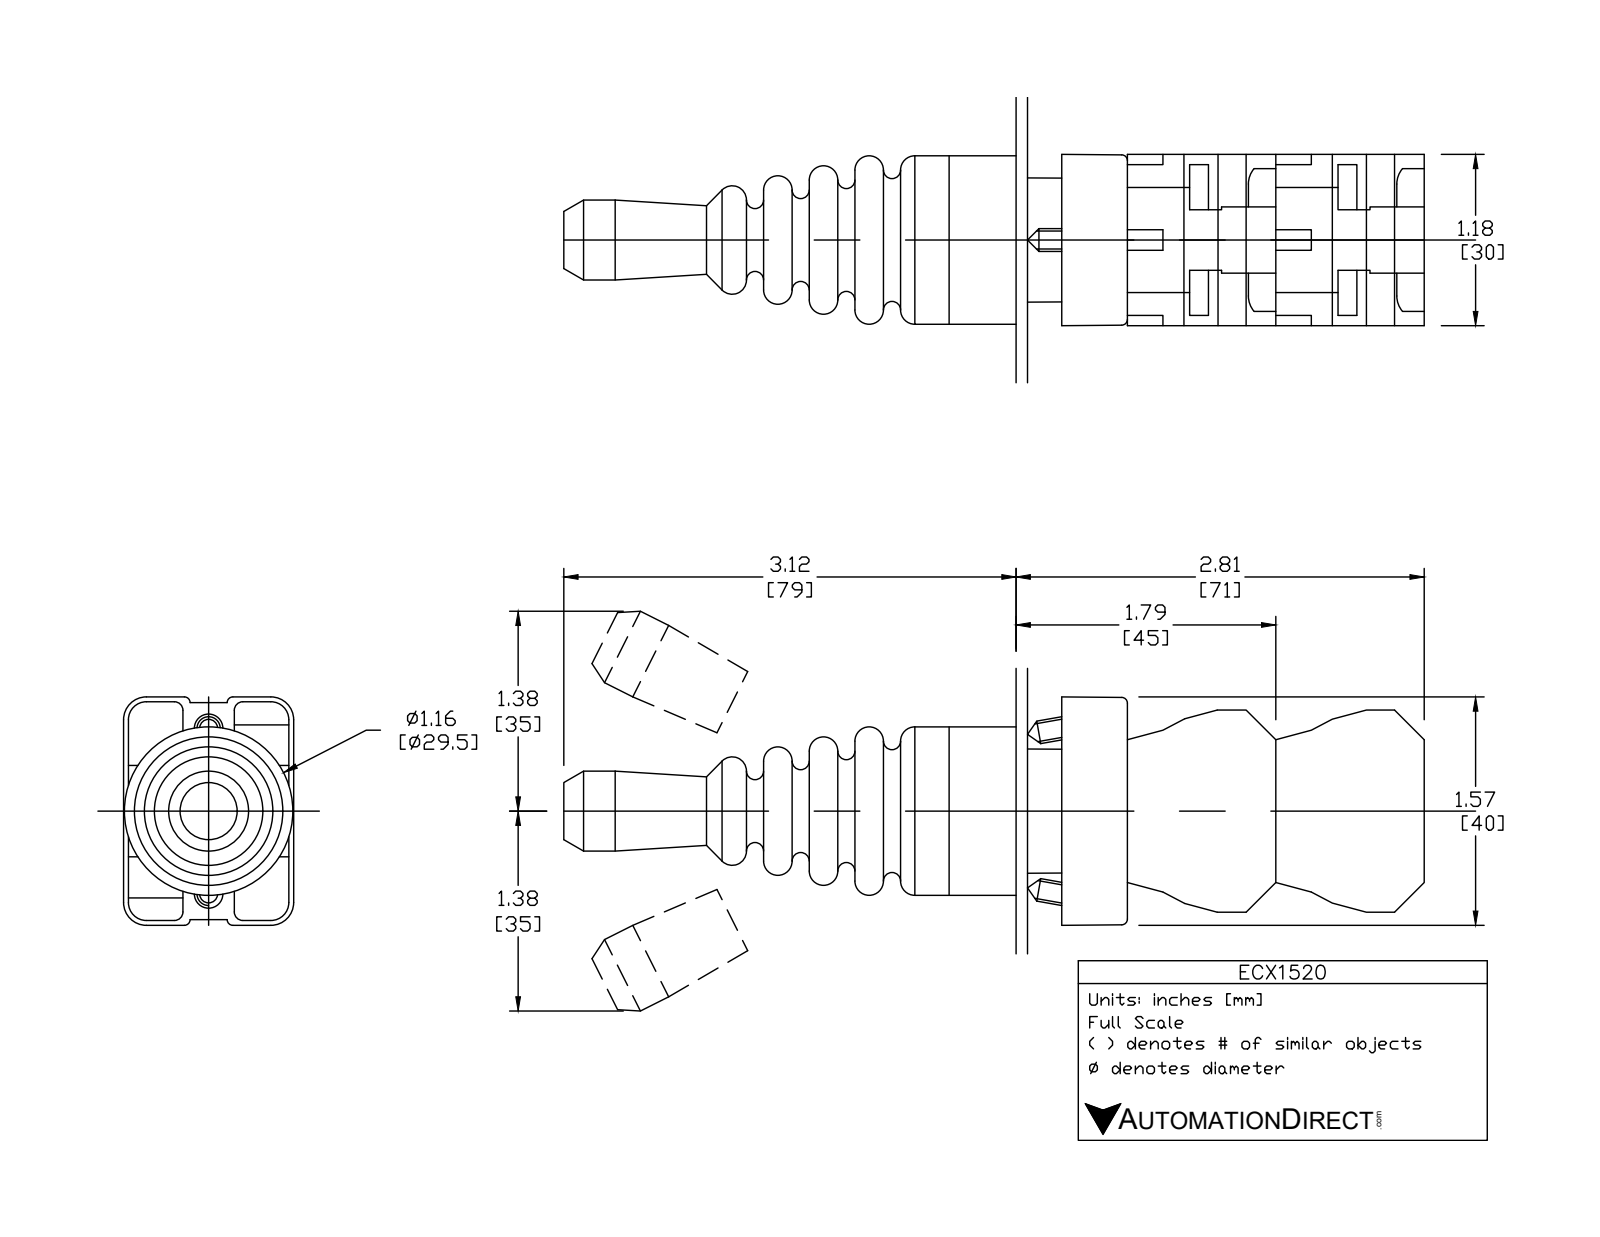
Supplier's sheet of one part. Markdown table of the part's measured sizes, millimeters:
| quantity | value |
| --- | --- |
| part name | ECX1520 |
| STEP written by | SolidWorks 2017 (AUTOMOTIVE_DESIGN) |
| units | millimeters |
| bodies | 9 solids, 707 faces (450 planar, 172 cylindrical, 85 other) |
| overall size | 150.1 × 40.2 × 30 |
| volume | 79 810 mm³ |
| surface area | 33 110 mm² |
| round holes (diameter × count) | 2 × 4, 2.2 × 2, 3.1 × 2, 3.3 × 2, 5 × 1, 22.3 × 1, 22.6 × 1 |
| round bosses / shafts (diameter × count) | 4 × 2, 30 × 1, 29.8 × 1, 24 × 1, 21.7 × 1, 19.8 × 1 |
| partial cylindrical surfaces (radius × count) | 1.5 × 24, 1 × 12, 3.1 × 12, 4 × 12, 1 × 4, 0.5 × 2, 1.6 × 2, 2 × 2 |
| main face-to-face distances | 15, 14.7, 26, 29.7, 30.3, 56.3, 0.8, 0.8, 7.8, 6.8 |
| hole center spacings | 6, 16.2, 15, 6.5, 12, 13.8, 19.2, 2.5 |
